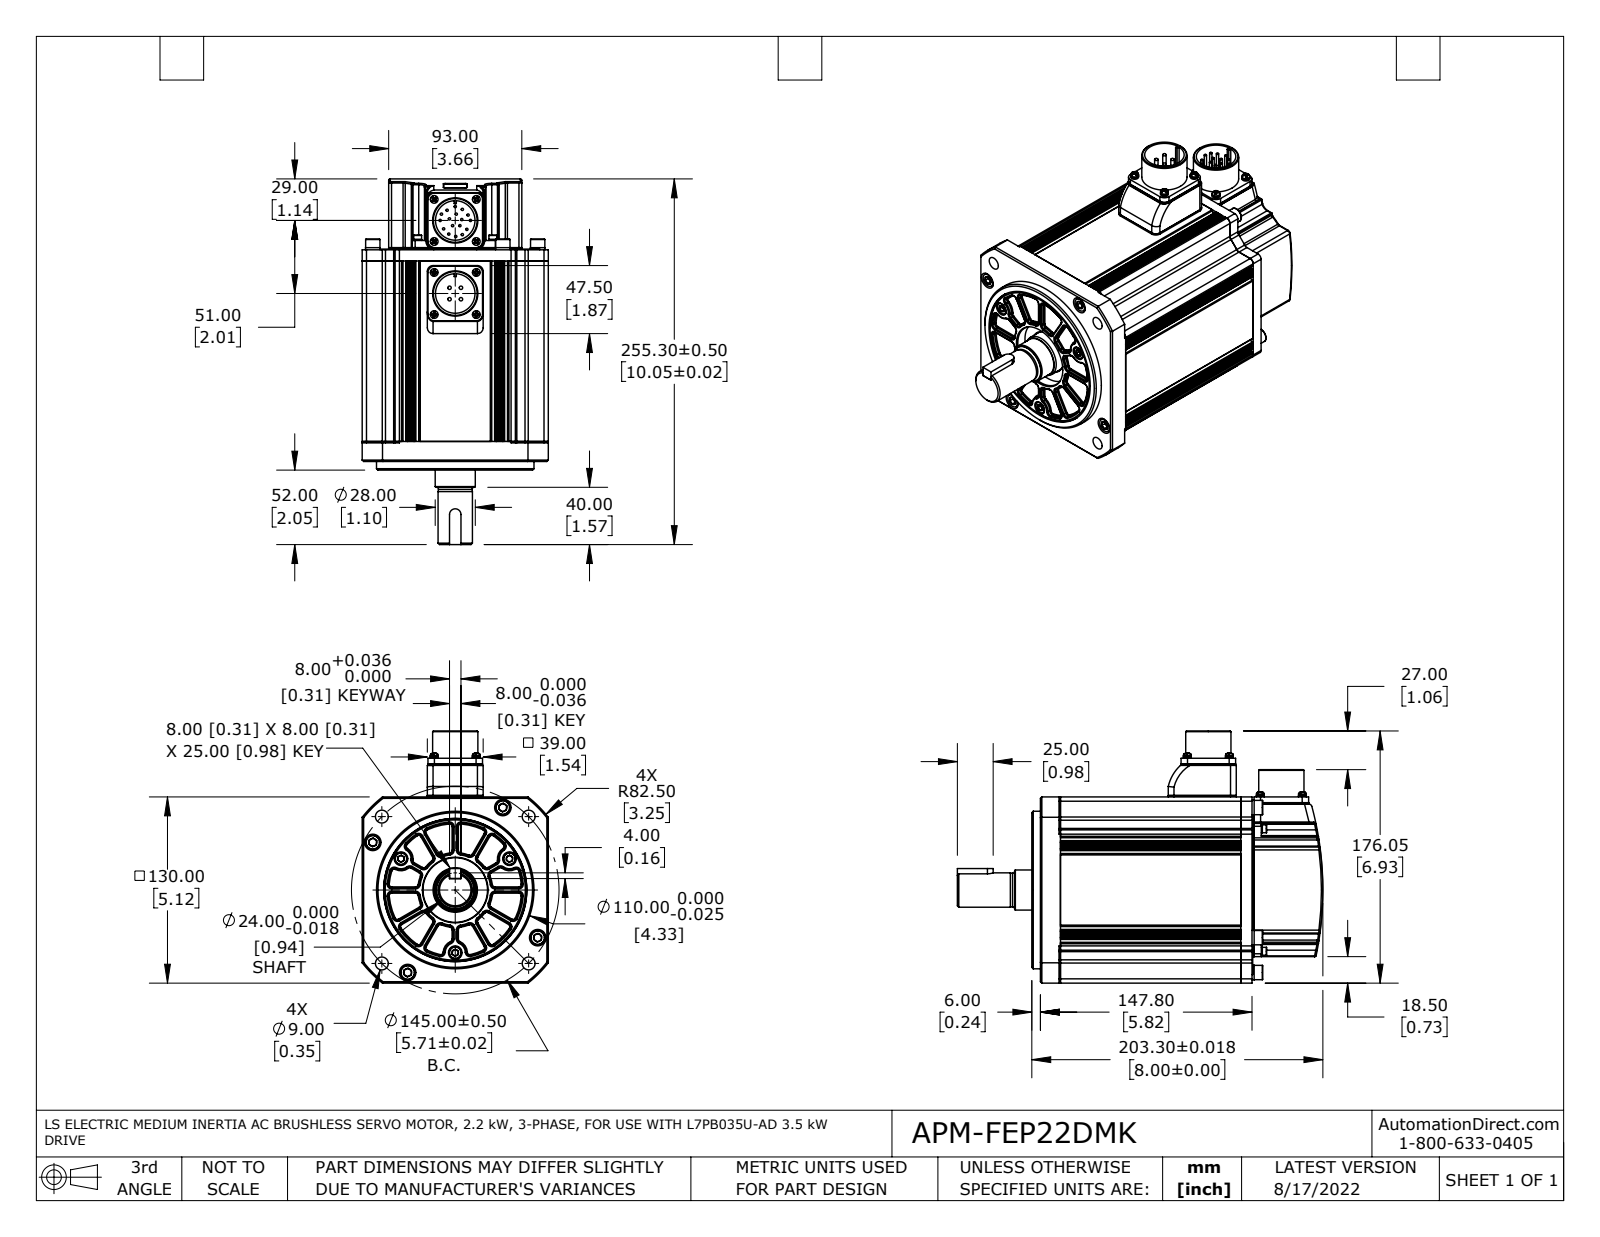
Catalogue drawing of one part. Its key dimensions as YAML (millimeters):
part_name: "FMP13GA001G04_Out Line(APM-FEP22D_K) r1 nc fxt"
step_written_by: "SolidWorks 2017 (AUTOMOTIVE_DESIGN)"
units: millimeters
bodies: {solids: 56, faces: 2133, planar: 706, cylindrical: 801, other: 626}
overall_size: [255.3, 176, 130]
volume: 2701000
surface_area: 313500
round_holes:
  - {diameter: 2.5, count: 12}
  - {diameter: 3, count: 8}
  - {diameter: 3, count: 8}
  - {diameter: 3.5, count: 8}
  - {diameter: 5, count: 7}
  - {diameter: 3.6, count: 4}
  - {diameter: 3.7, count: 4}
  - {diameter: 6.8, count: 4}
  - {diameter: 7, count: 4}
  - {diameter: 9, count: 4}
  - {diameter: 11.5, count: 4}
  - {diameter: 5.6, count: 3}
round_bosses_or_shafts:
  - {diameter: 1.6, count: 17}
  - {diameter: 5.4, count: 8}
  - {diameter: 10.2, count: 4}
  - {diameter: 10, count: 4}
  - {diameter: 6, count: 4}
  - {diameter: 5.5, count: 4}
  - {diameter: 3, count: 4}
  - {diameter: 2.4, count: 4}
partial_cylinders:
  - {radius: 0.5, count: 72}
  - {radius: 2.5, count: 54}
  - {radius: 0.7, count: 24}
  - {radius: 2, count: 17}
  - {radius: 3, count: 16}
  - {radius: 1, count: 14}
  - {radius: 4.5, count: 12}
  - {radius: 4, count: 9}
face_to_face_distances: [126, 1, 130, 135.3, 8.3, 134.3, 9.3, 145.8, 144.8, 136.5]
hole_center_spacings: [20.8, 29.4, 51, 19.1, 26.4, 39.2, 41.6, 50.2]
